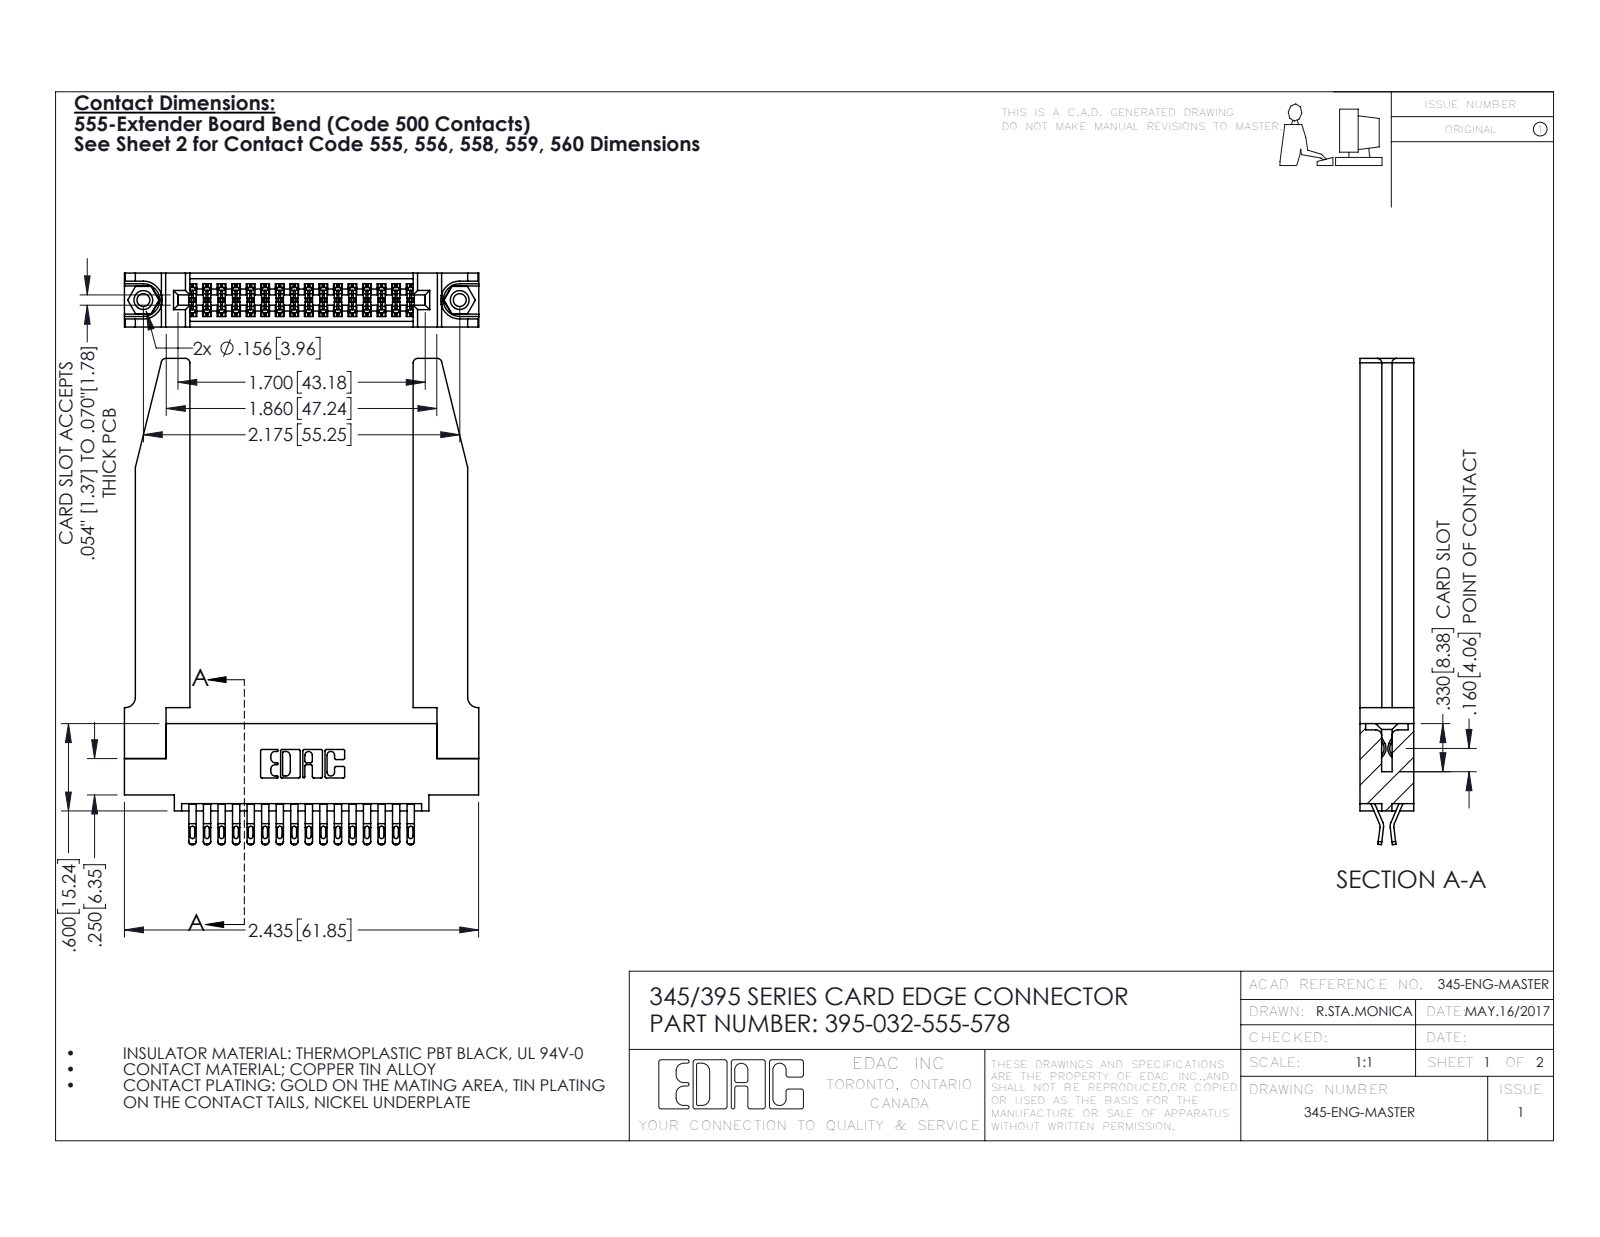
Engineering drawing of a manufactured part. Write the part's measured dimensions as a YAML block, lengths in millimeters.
part_name: "345 Part_0.110 Offset - 0.156 Dia-TH; 345-250-001_345-250-001-102; 395-032-555-578; 345-292-001_555 Tail (+1 more)"
step_written_by: "SolidWorks 2016 (CONFIG_CONTROL_DESIGN)"
units: millimeters
bodies: {solids: 37, faces: 2156, planar: 1218, cylindrical: 886, other: 52}
overall_size: [84.9, 61.9, 9.4]
volume: 13600
surface_area: 15310
round_holes:
  - {diameter: 2.3, count: 2}
  - {diameter: 3.2, count: 2}
  - {diameter: 4, count: 2}
  - {diameter: 1.6, count: 1}
round_bosses_or_shafts:
  - {diameter: 3.9, count: 2}
partial_cylinders:
  - {radius: 0.4, count: 80}
  - {radius: 0.5, count: 64}
  - {radius: 0.2, count: 48}
  - {radius: 0.3, count: 22}
  - {radius: 0.8, count: 8}
  - {radius: 0.2, count: 6}
  - {radius: 0.8, count: 6}
  - {radius: 0.7, count: 3}
face_to_face_distances: [9.4, 1.8, 7.6, 0.6, 3.8, 3.8, 5.1, 2.5, 6.9, 5.6]
hole_center_spacings: [6.9, 49.3, 55.2]
